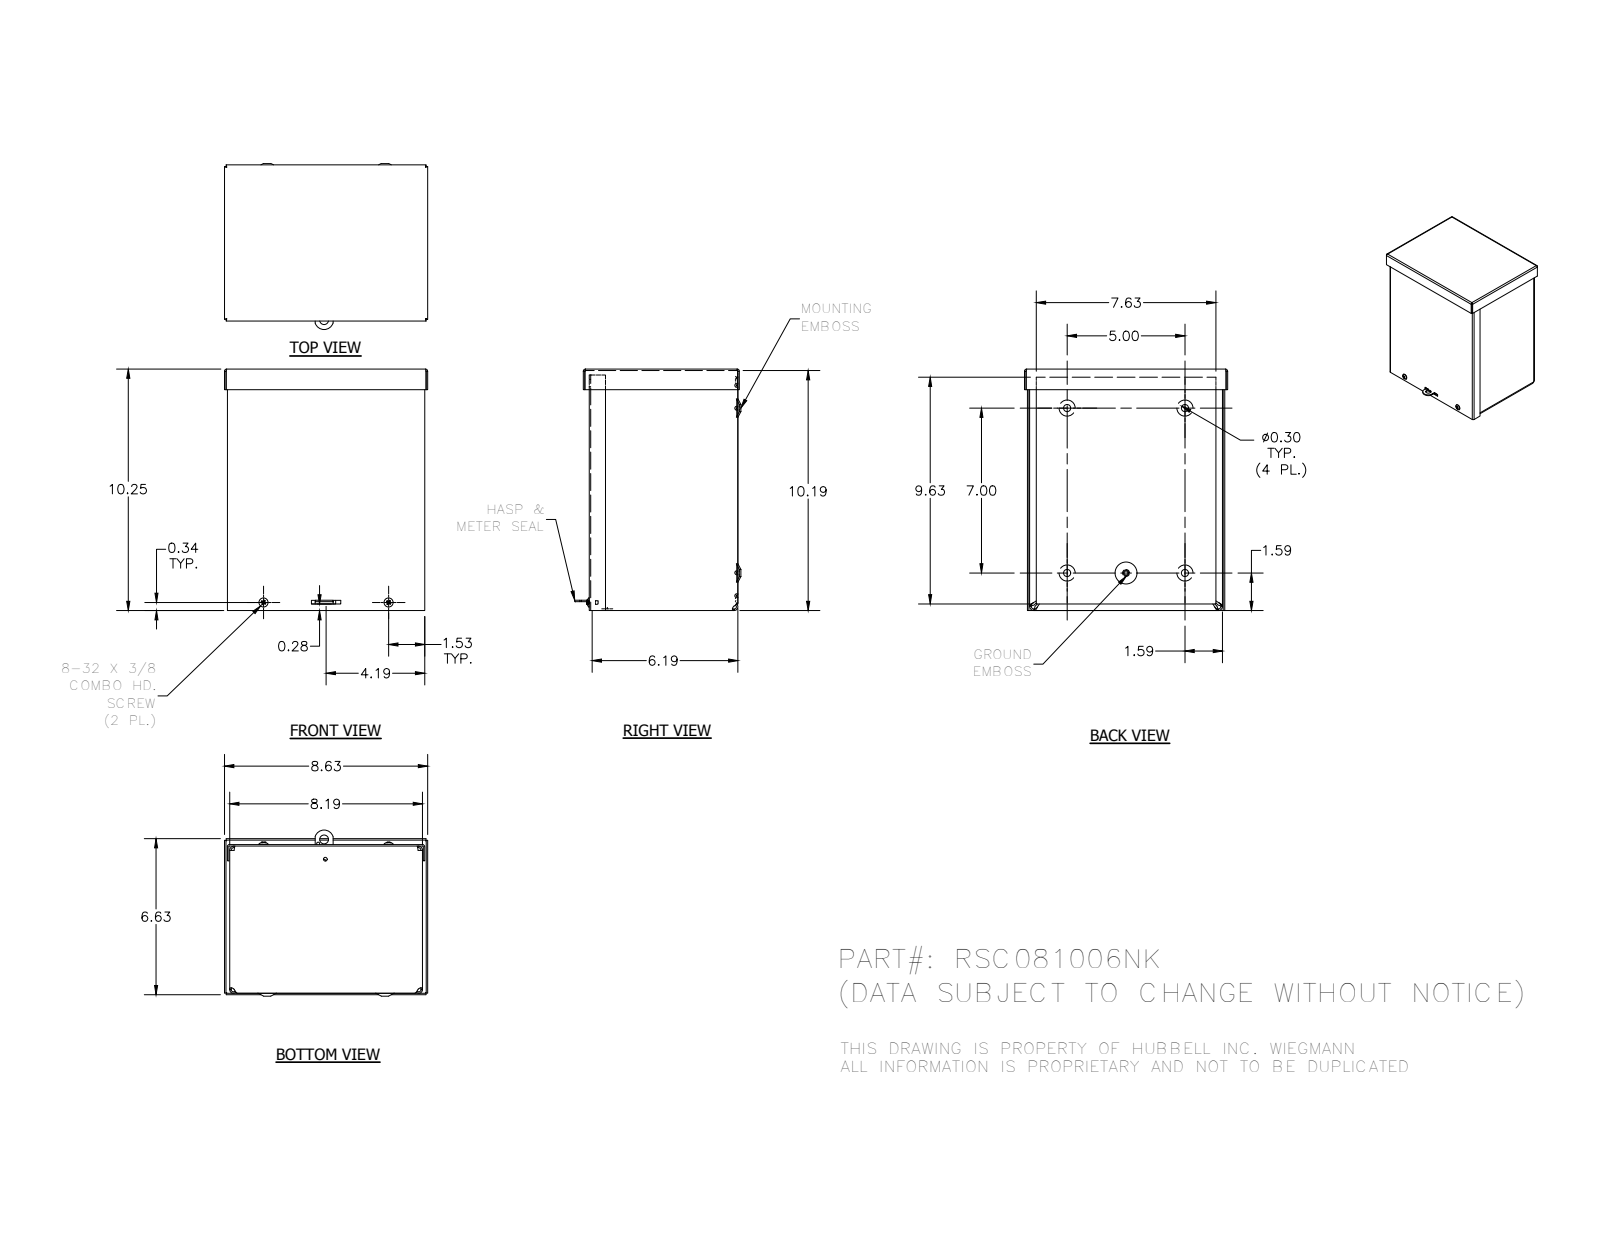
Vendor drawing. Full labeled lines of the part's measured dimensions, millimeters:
Part name (STEP PRODUCT): RSC081006NK_WRAP; RSC0810NK_LID; RSC0806NK_CAP; 3183 (+3 more)
STEP written by: Autodesk Inventor 2014 (AUTOMOTIVE_DESIGN)
Units: millimetres
Bodies: 7 solids, 377 faces (163 planar, 78 cylindrical, 136 other)
Overall size (bounding box): 260.36 × 219.07 × 180.97
Volume: 534 077 mm³ · Surface area: 687 040 mm²
Round holes (diameter × count): ⌀7.62 ×4, ⌀7.95 ×4, ⌀3.76 ×2, ⌀3.17 ×1, ⌀3.45 ×1, ⌀3.96 ×1, ⌀4.19 ×1, ⌀9.52 ×1
Round bosses / shafts (diameter × count): ⌀9.75 ×2, ⌀4.17 ×2, ⌀5.8 ×1
Partial cylindrical surfaces — rounded edges, fillets, slot ends (radius × count): R0.79 ×8, R2.37 ×8, R3.17 ×8, R4.75 ×8, R1.4 ×4, R1.57 ×4, R2.38 ×4, R2.97 ×4
Main face-to-face distances: 1.58, 1.57, 206.39, 158.73, 257.19, 157.15, 1.59, 3.15, 160.32, 158.74
Hole centre spacings: 27.24, 32.03, 63.5, 127, 134.95, 177.8, 188.79, 204.79
